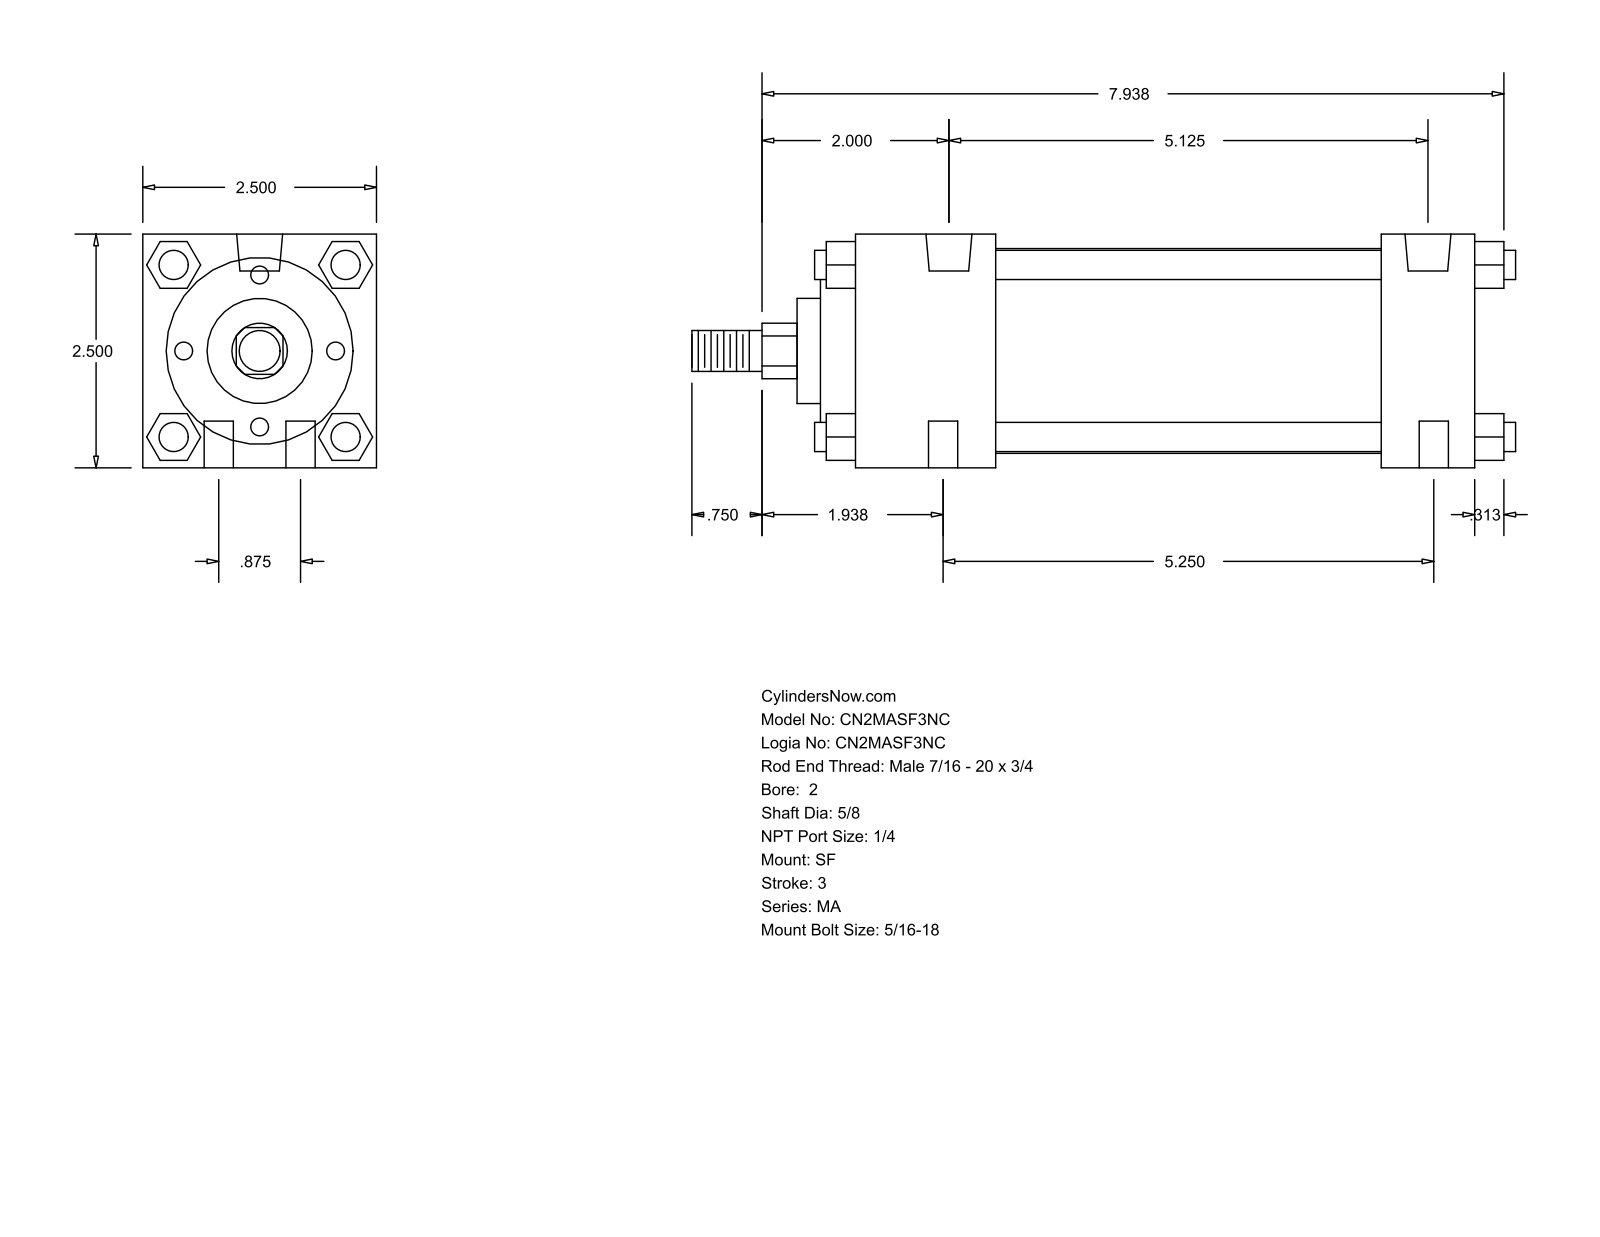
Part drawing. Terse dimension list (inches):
name: MA_SF__0200_0.625
written by: GSSL Pune (CONFIG_CONTROL_DESIGN)
unit: in
bodies: 0 solids, 126 faces (95 planar, 31 cylindrical, 0 other)
size: 8.813 × 2.5 × 2.5
holes: 6× ⌀0.313, 2× ⌀0.492
bosses: 4× ⌀0.313, 1× ⌀2.19, 1× ⌀2, 1× ⌀1.125, 1× ⌀0.625, 1× ⌀0.437
rounds: 1× R0.297
face distances: 2.5, 1, 0.5, 1.5, 6.625, 5.625, 4.125, 5.125, 0.375, 1.875
hole spacings: 0.442, 5.206, 0.875, 5.125, 5.25, 5.322
